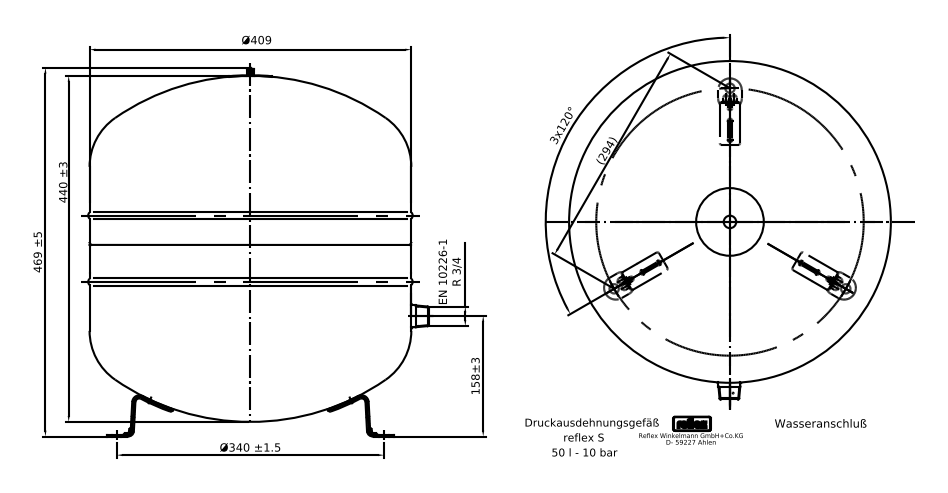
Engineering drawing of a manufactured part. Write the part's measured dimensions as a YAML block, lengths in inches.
step_written_by: "Mechanical Desktop 2011 (CONFIG_CONTROL_DESIGN)"
units: inches
bodies: {solids: 16, faces: 208, planar: 79, cylindrical: 76, other: 53}
overall_size: [18.484, 17.26, 16.449]
volume: 2899
surface_area: 1891
round_holes:
  - {diameter: 0.591, count: 3}
  - {diameter: 0.222, count: 1}
round_bosses_or_shafts:
  - {diameter: 16.102, count: 1}
  - {diameter: 1.327, count: 1}
  - {diameter: 0.269, count: 1}
  - {diameter: 0.142, count: 1}
  - {diameter: 0.094, count: 1}
partial_cylinders:
  - {radius: 5.842, count: 9}
  - {radius: 5.92, count: 9}
  - {radius: 0.591, count: 6}
  - {radius: 0.089, count: 4}
  - {radius: 0.035, count: 3}
  - {radius: 0.061, count: 2}
  - {radius: 0.106, count: 2}
  - {radius: 0.146, count: 2}
face_to_face_distances: [8.268, 4.134, 5.236, 9.37, 13.504, 0.079, 5.157, 9.291, 13.425, 1.102]
hole_center_spacings: [6.693, 11.593, 11.592]
